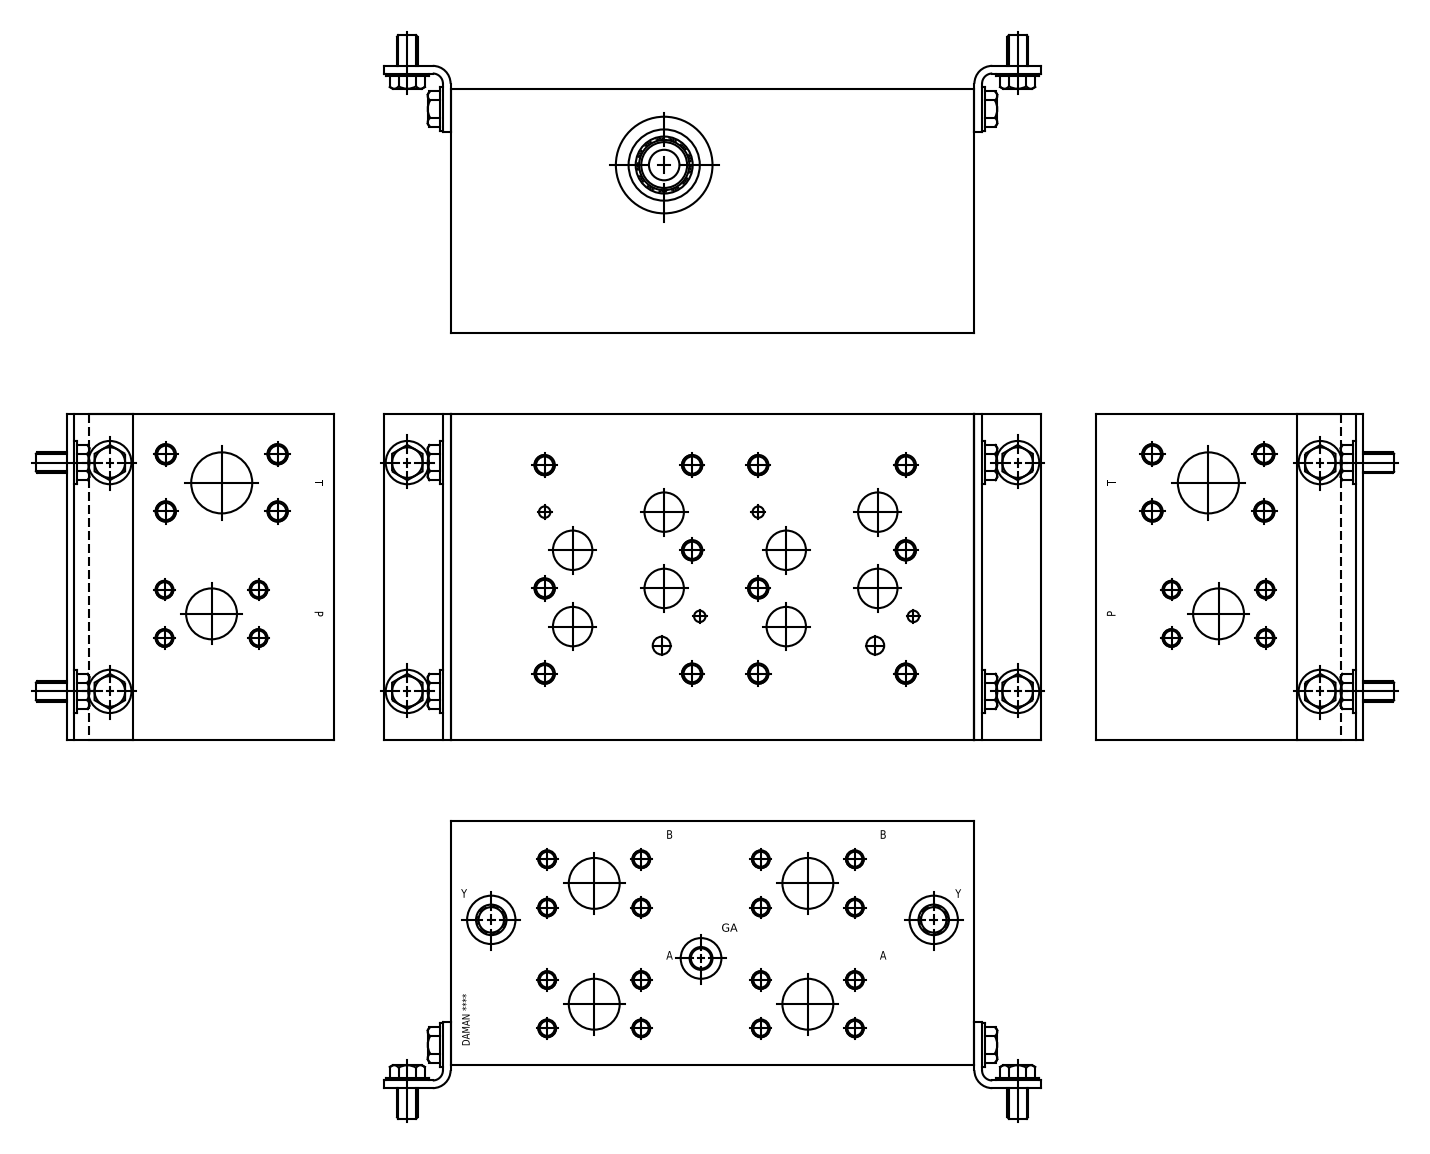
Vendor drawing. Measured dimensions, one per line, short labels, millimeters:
name: Part_AD08HP025F~C_3D
written by: Autodesk Inventor 2019 (AUTOMOTIVE_DESIGN)
unit: mm
bodies: 1 solid, 816 faces (424 planar, 140 cylindrical, 252 other)
size: 327.02 × 203.2 × 152.4
volume: 9 730 000 mm³; area: 380 245 mm²
holes: 24× ⌀11.13, 22× ⌀9.35, 20× ⌀12.7, 18× ⌀10.72, 8× ⌀24.61, 5× ⌀31.75, 4× ⌀7.14, 3× ⌀19.05, 2× ⌀17.5, 2× ⌀19.25, 2× ⌀30.63, 1× ⌀12.29
face distances: 152.4, 203.2, 327.02, 191.29, 11.91, 0.79, 190.5, 202.41, 30.23, 28.45
hole spacings: 33.01, 133.35, 30.18, 75.41, 153.2, 95.14, 58.72, 66.02
